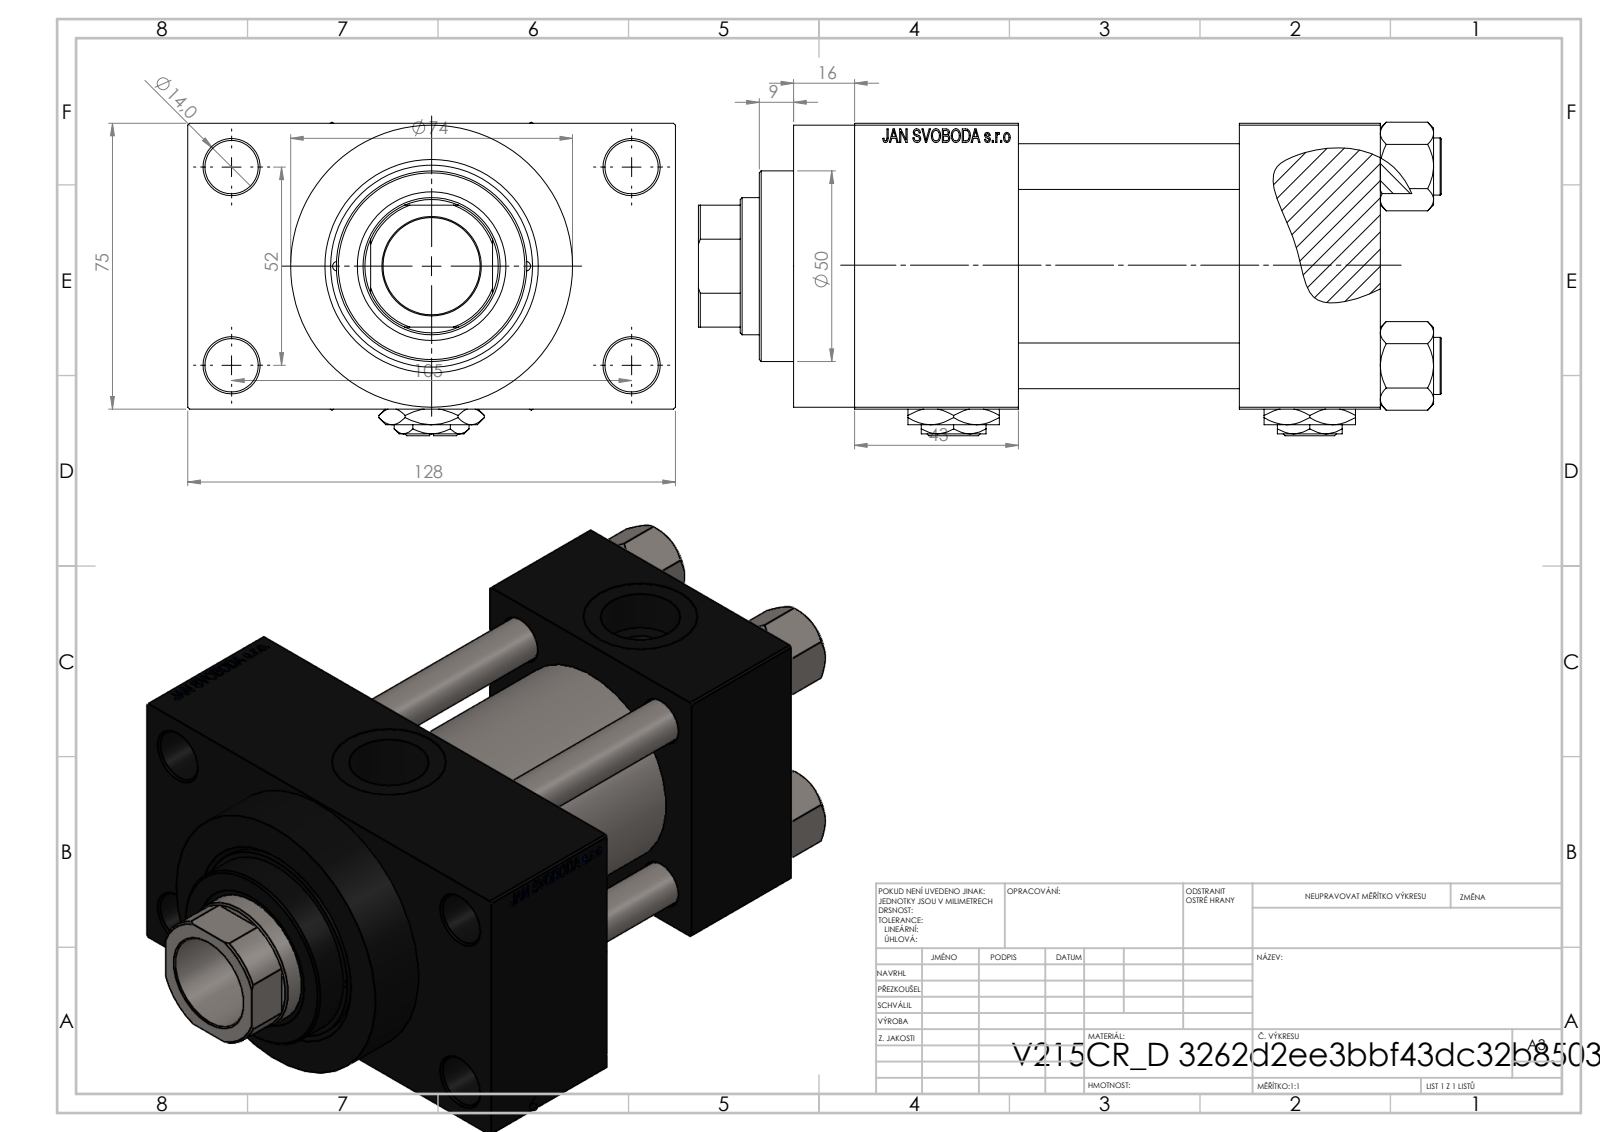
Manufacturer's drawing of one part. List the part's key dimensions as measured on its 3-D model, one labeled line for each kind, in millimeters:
Part name (STEP PRODUCT): V215CR_D_Body; V215CR_D_TYCINKA; V215_VC_A; V215CR_VCP_D (+2 more)
STEP written by: SolidWorks 2019 (CONFIG_CONTROL_DESIGN)
Units: millimetres
Bodies: 13 solids, 1215 faces (549 planar, 104 cylindrical, 562 other)
Overall size (bounding box): 195 × 128 × 82.27
Volume: 821 732 mm³ · Surface area: 177 975 mm²
Round holes (diameter × count): ⌀12 ×4, ⌀14 ×4, ⌀2.5 ×2, ⌀7 ×2, ⌀20.96 ×2, ⌀30 ×2, ⌀25.5 ×1, ⌀36 ×1, ⌀39 ×1, ⌀41 ×1, ⌀53 ×1
Round bosses / shafts (diameter × count): ⌀15 ×4, ⌀74 ×1, ⌀56 ×1, ⌀50 ×1
Partial cylindrical surfaces — rounded edges, fillets, slot ends (radius × count): R17.5 ×1
Main face-to-face distances: 75, 58, 37, 95, 101.5, 26.5, 138, 43, 101, 128
Hole centre spacings: 26.19, 26.35, 36.98, 38.03, 52.3, 57.22, 58.43, 58.59
